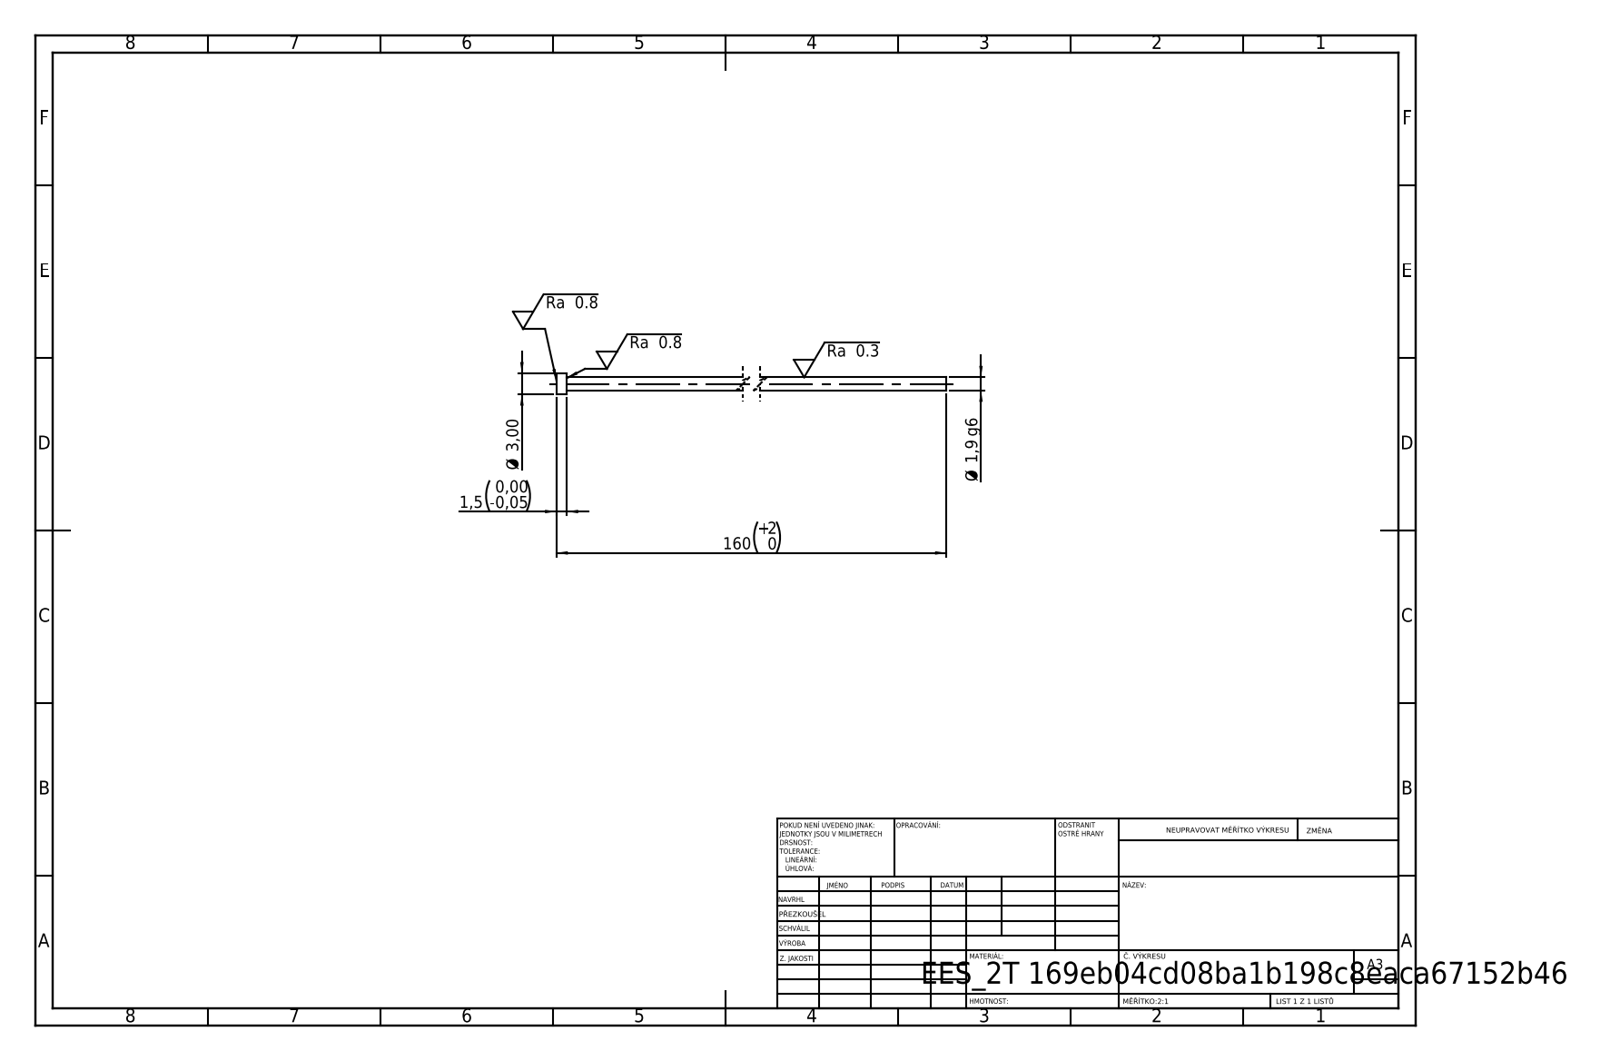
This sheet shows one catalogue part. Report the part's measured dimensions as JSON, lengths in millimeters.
{"step_written_by": "SolidWorks 2019 (CONFIG_CONTROL_DESIGN)", "units": "millimeters", "bodies": {"solids": 1, "faces": 7, "planar": 3, "cylindrical": 4, "other": 0}, "overall_size": [160, 3, 3], "volume_mm3": 460, "surface_area_mm2": 974, "round_bosses_or_shafts": [[3, 1], [1.9, 1]], "face_to_face_distances": [1.5, 160, 158.5]}
